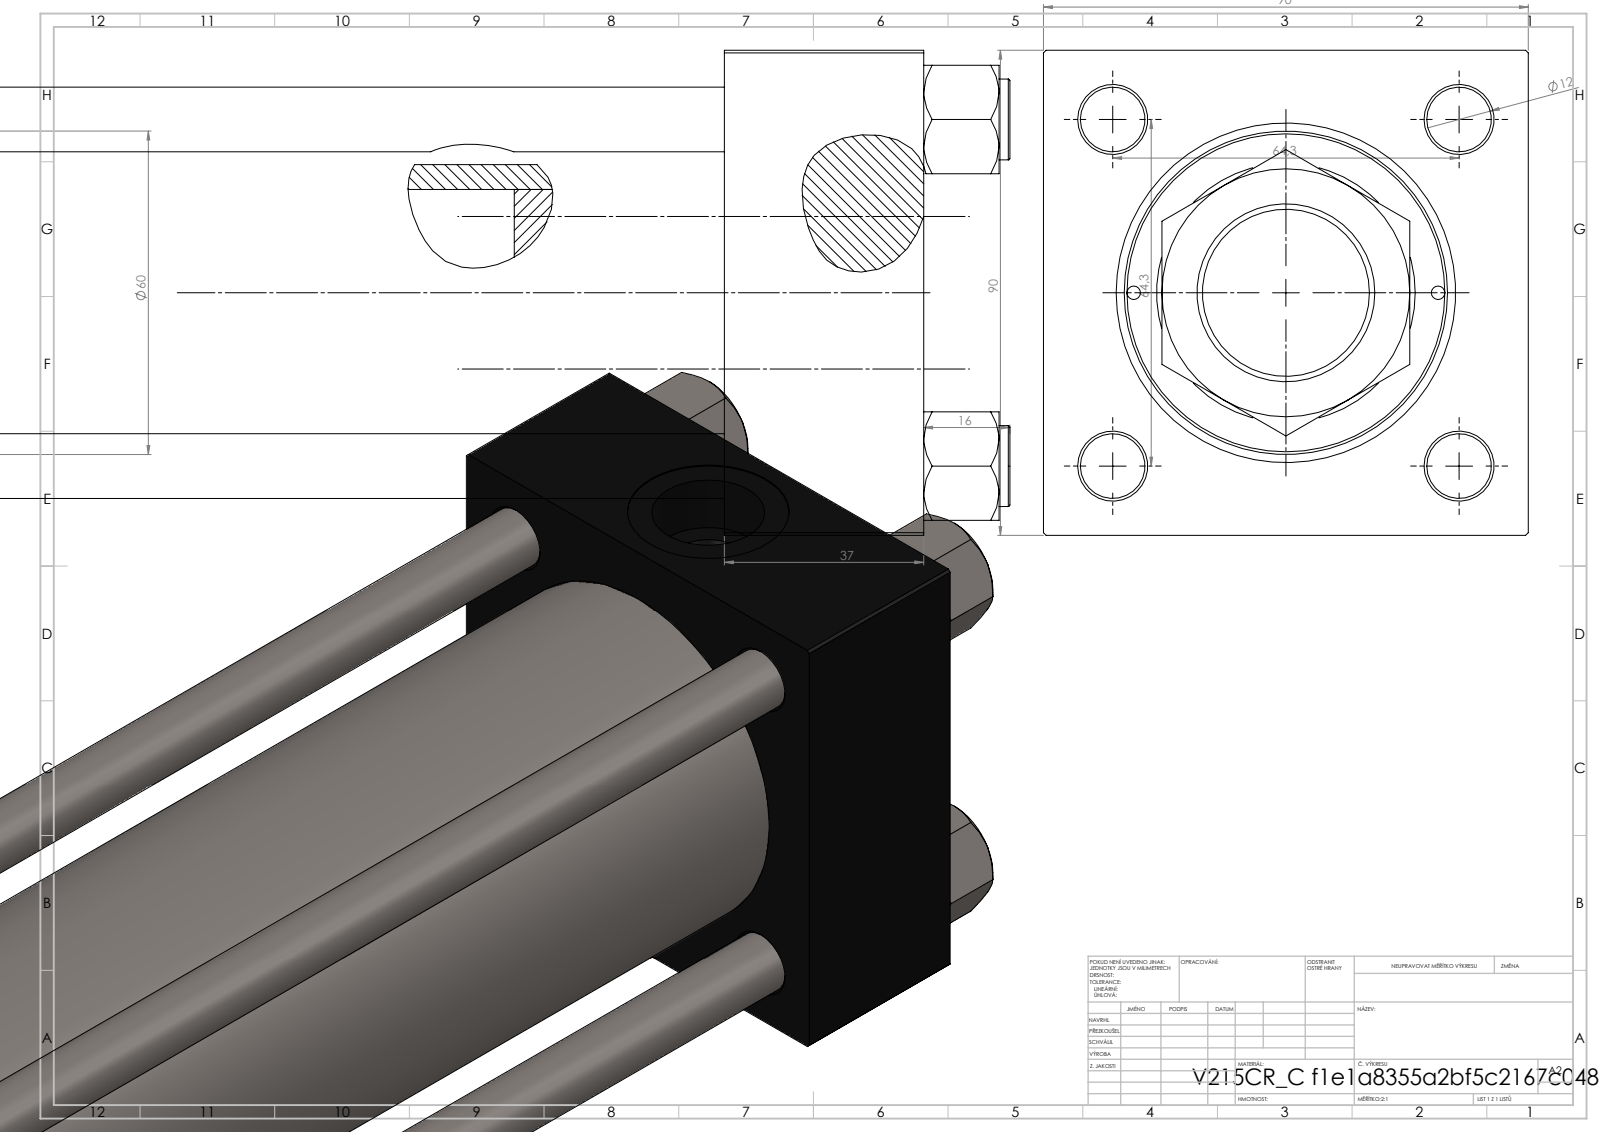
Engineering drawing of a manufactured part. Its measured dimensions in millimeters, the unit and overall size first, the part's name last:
Units: millimetres
Overall size (bounding box): 606 × 90 × 90
Round holes (diameter × count): ⌀12 ×4, ⌀2.5 ×2, ⌀7 ×2, ⌀20.96 ×2, ⌀30 ×2, ⌀31.5 ×1, ⌀45 ×1, ⌀48 ×1, ⌀50 ×1, ⌀60 ×1, ⌀63 ×1
Round bosses / shafts (diameter × count): ⌀15 ×4, ⌀69 ×1, ⌀33 ×1, ⌀31 ×1
Partial cylindrical surfaces — rounded edges, fillets, slot ends (radius × count): R22 ×1
Main face-to-face distances: 90, 37, 59, 426, 389, 485, 448, 46, 480, 32
Hole centre spacings: 32.39, 45.47, 64.3, 68.42, 28.25, 90.93, 56.5, 427.5
Volume: 1 966 000 mm³ · Surface area: 436 143 mm²
Bodies: 12 solids, 1201 faces (542 planar, 93 cylindrical, 566 other)
Part name (STEP PRODUCT): NUT_M5_C; MTA; V215CR_C_TYCINKA; V215CR_VCP_C (+2 more)
STEP written by: SolidWorks 2019 (CONFIG_CONTROL_DESIGN)
